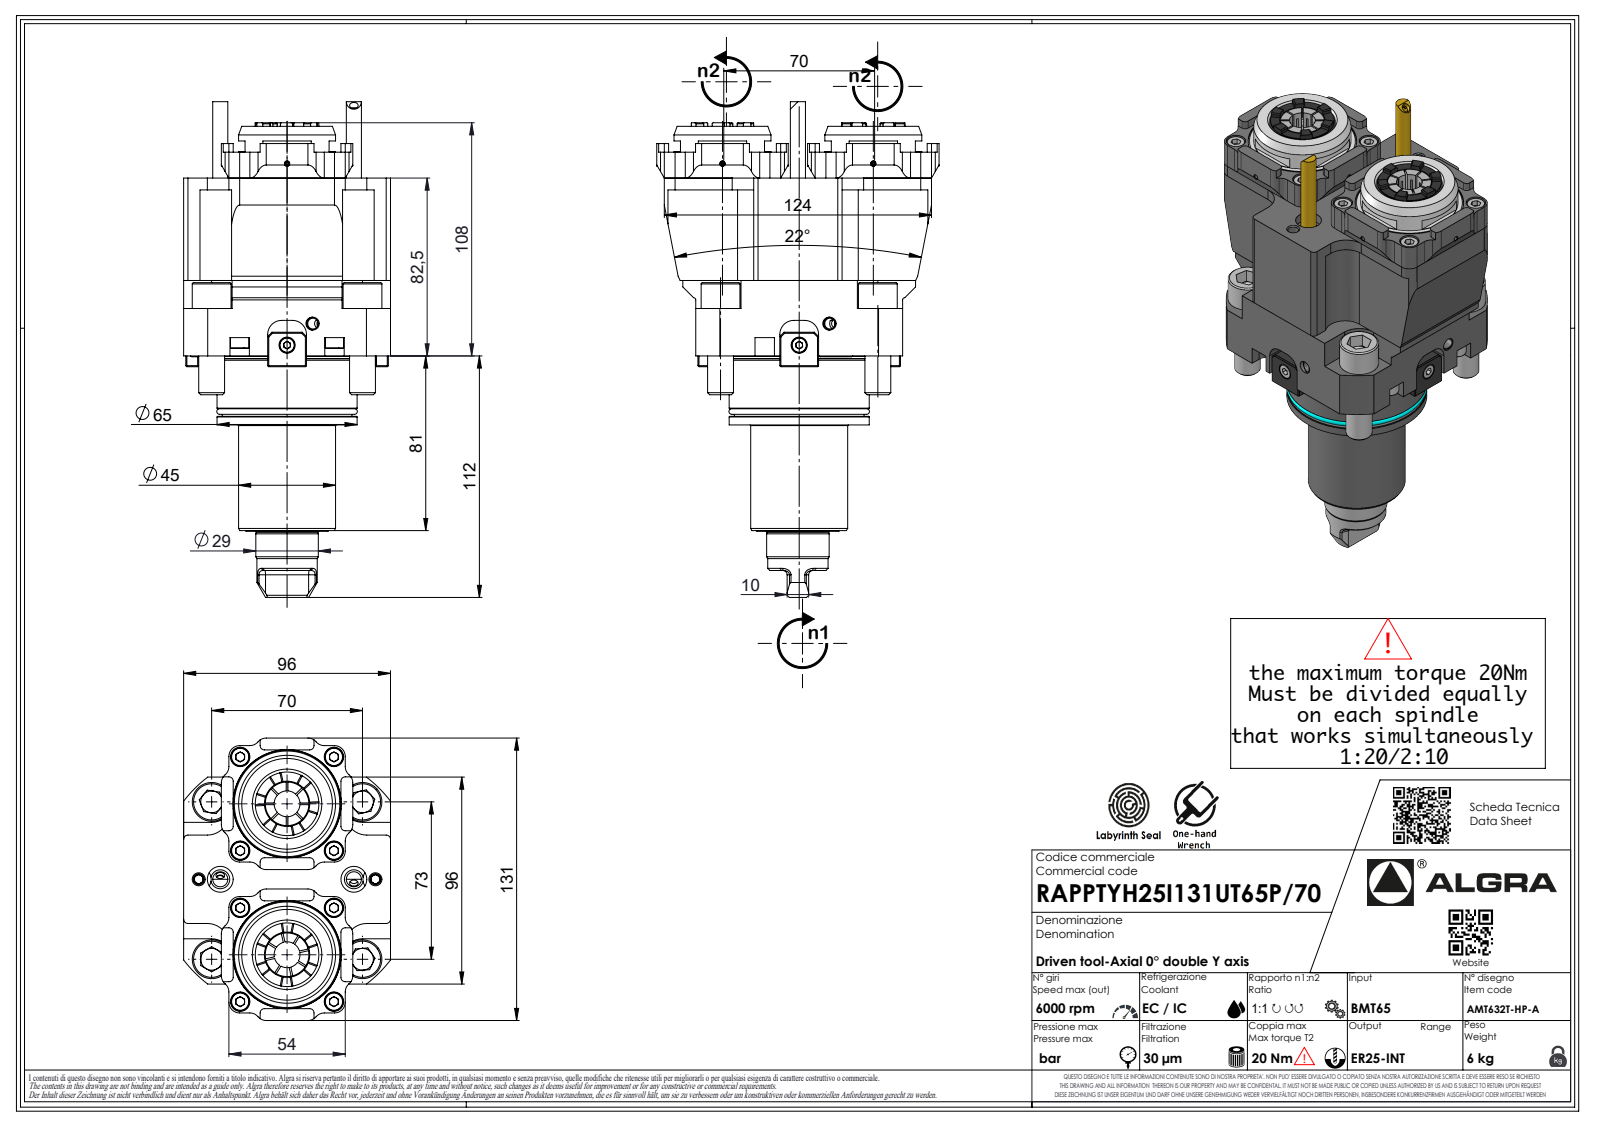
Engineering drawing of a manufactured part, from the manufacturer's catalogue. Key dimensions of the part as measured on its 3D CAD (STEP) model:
Part name (STEP PRODUCT): RAPPTYH25I131UT65P70
STEP written by: SolidWorks 2023 (AUTOMOTIVE_DESIGN)
Units: millimetres
Bodies: 5 solids, 843 faces (492 planar, 189 cylindrical, 162 other)
Overall size (bounding box): 237.78 × 131 × 96
Volume: 1 033 000 mm³ · Surface area: 90 379 mm²
Round holes (diameter × count): ⌀4 ×2, ⌀2.1 ×1
Round bosses / shafts (diameter × count): ⌀12 ×4, ⌀45 ×3, ⌀11.57 ×2, ⌀7 ×2, ⌀6 ×2, ⌀65 ×1, ⌀64.6 ×1, ⌀60.2 ×1
Partial cylindrical surfaces — rounded edges, fillets, slot ends (radius × count): R5 ×40, R2 ×28, R35 ×20, R0.33 ×7, R0.52 ×7, R3.7 ×7, R9.25 ×4, R10 ×4
Main face-to-face distances: 96, 22.25, 73.75, 12, 82.5, 51.5, 24, 106.5, 71.5, 47.5
